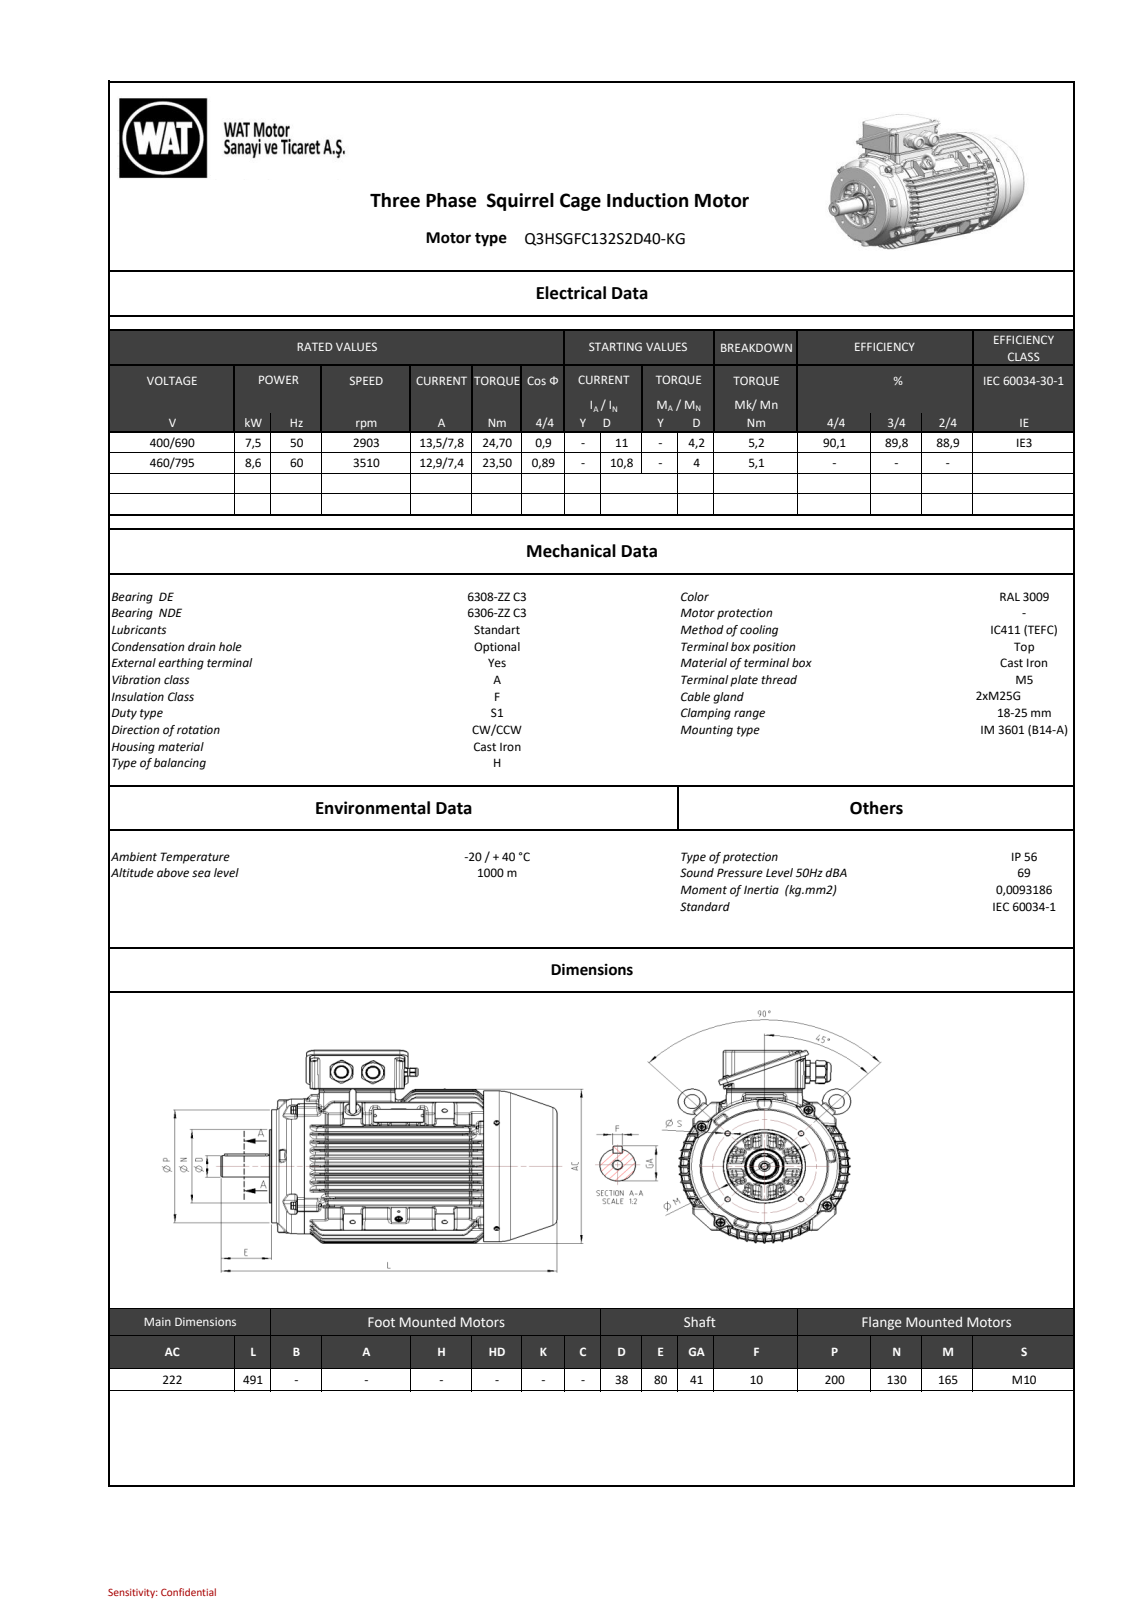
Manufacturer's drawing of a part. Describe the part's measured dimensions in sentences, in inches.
The part is named "260021E4F5C7p85i". Its 3-D file was written by "SIEMENS PLM Software NX 11.0 (AUTOMOTIVE_DESIGN)". It is 0 solids with 4332 faces: 894 planar, 1200 cylindrical and 2238 other. Overall it measures 19.331 by 11.412 by 8.72 inches. Round holes: 10 of diameter 0.197, 6 of diameter 0.268, 4 of diameter 0.335, 4 of diameter 0.394, 2 of diameter 0.098, 2 of diameter 0.677, 1 of diameter 0.236, 1 of diameter 0.315, 1 of diameter 0.402, 1 of diameter 0.445, 1 of diameter 0.512, 1 of diameter 2.299. Round bosses or shafts: 4 of diameter 0.394, 4 of diameter 0.341, 4 of diameter 0.315, 4 of diameter 0.157, 2 of diameter 1.091, 2 of diameter 0.994, 2 of diameter 0.787, 2 of diameter 0.472. Partial cylindrical surfaces (rounded edges, fillets, slot ends): 264 of radius 0.157, 118 of radius 0.02, 96 of radius 0.059, 82 of radius 0.118, 26 of radius 0.039, 24 of radius 0.071, 24 of radius 0.079, 7 of radius 0.01. The main face-to-face distances are 0.516, 1.035, 0.519, 1.557, 1.041, 0.522, 3.565, 2.081, 1.565, 1.046. The hole center spacings are 2.571, 0.838, 3.819, 4.564, 5.401, 5.426, 7.041, 1.326.
